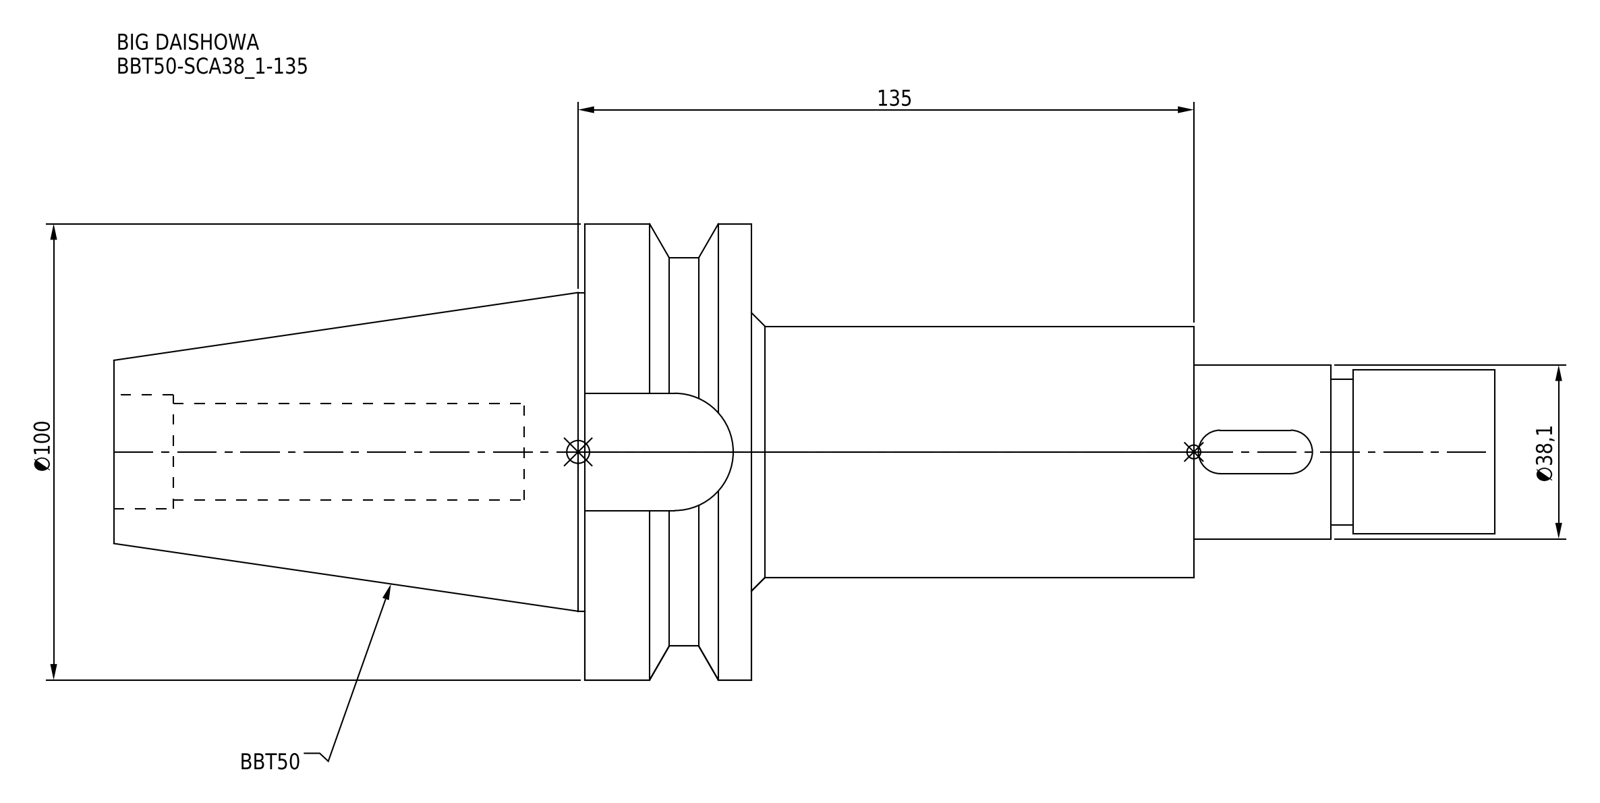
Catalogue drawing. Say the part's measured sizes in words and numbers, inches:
The part is named "BBT50-SCA38_1-135". Its 3-D file was written by "CREO PARAMETRIC BY PTC INC, 2016380 (AUTOMOTIVE_DESIGN)". It is 1 solid with 42 faces: 12 planar, 22 cylindrical and 8 other. Overall it measures 11.921 by 3.937 by 3.937 inches. Its volume is 47.9 cubic inches and its surface area 117.2 square inches. Round holes: 1 of diameter 0.835, 1 of diameter 0.984. Round bosses or shafts: 1 of diameter 3.937, 1 of diameter 3.346, 1 of diameter 2.75, 1 of diameter 2.165, 1 of diameter 1.5, 1 of diameter 1.417, 1 of diameter 1.26. Partial cylindrical surfaces (rounded edges, fillets, slot ends): 2 of radius 0.187. The main face-to-face distances are 1.437, 3.819, 5.256, 2.598, 6.417, 7.854, 11.921, 9.323, 5.504, 4.067.
